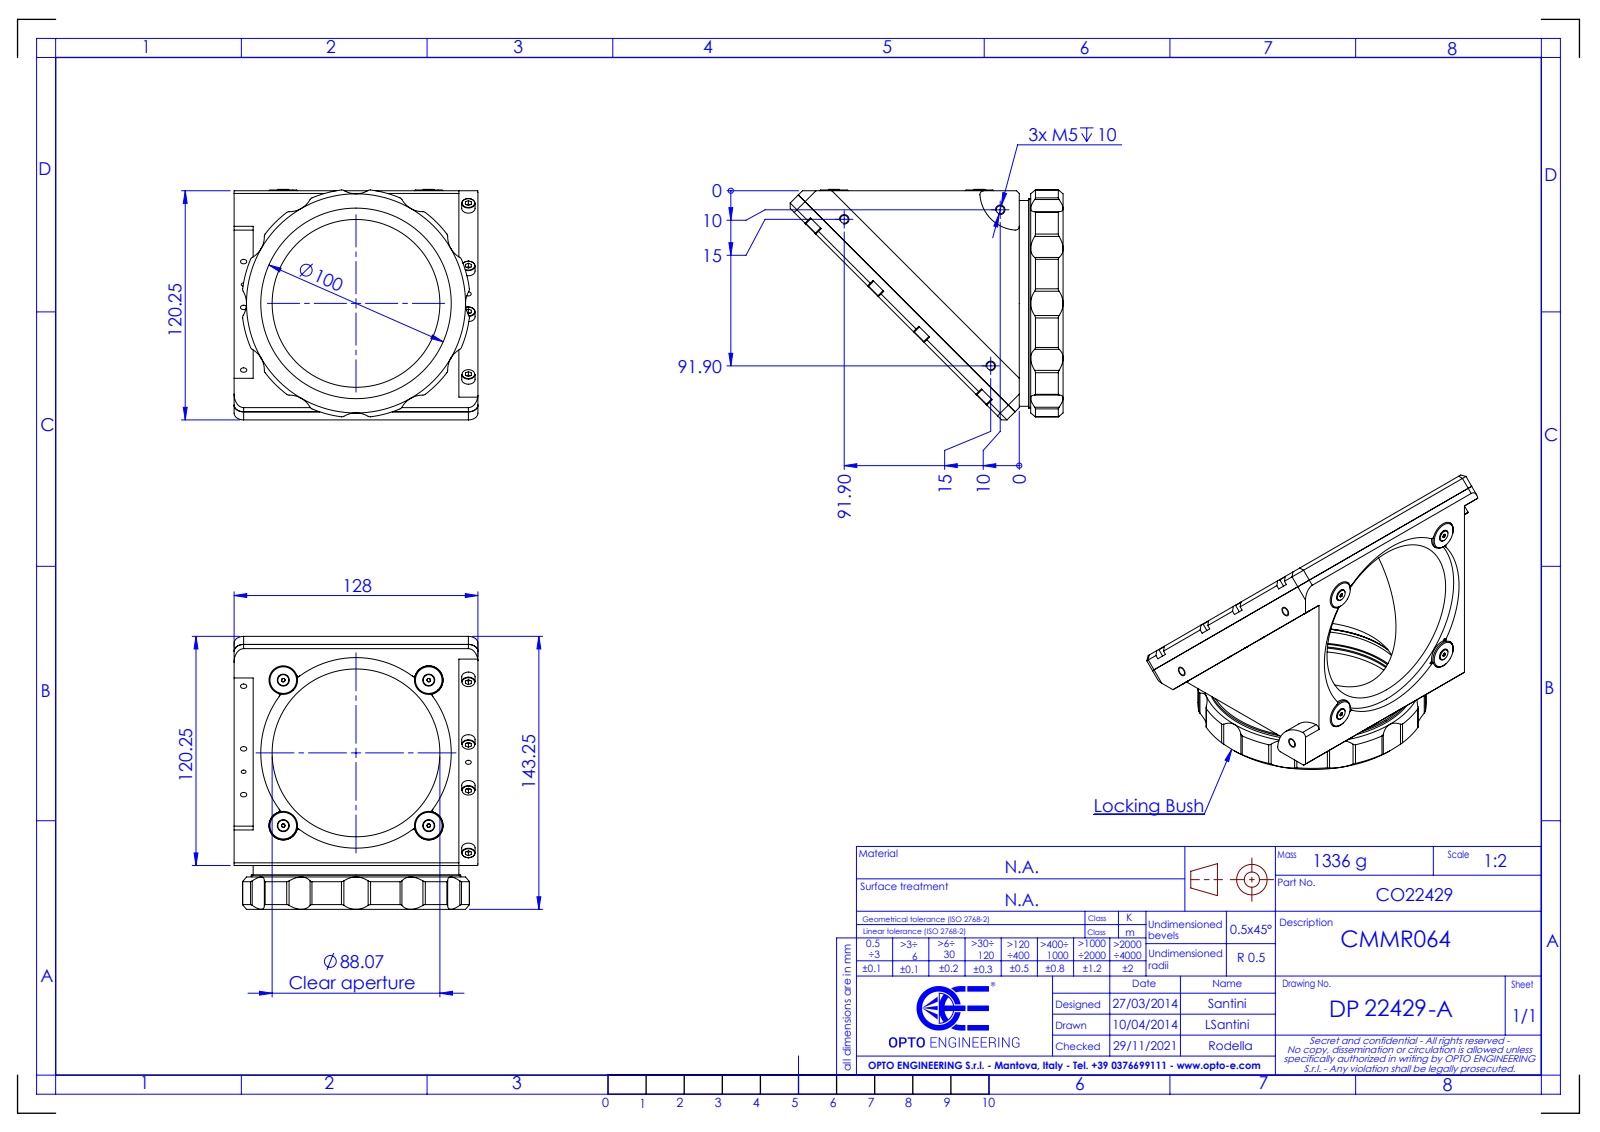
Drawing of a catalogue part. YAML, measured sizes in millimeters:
part_name: "DP22429 -A_CMMR064"
step_written_by: "SolidWorks 2021 (CONFIG_CONTROL_DESIGN)"
units: millimeters
bodies: {solids: 0, faces: 406, planar: 138, cylindrical: 178, other: 90}
overall_size: [143.25, 128, 120.98]
round_holes:
  - {diameter: 3.3, count: 8}
  - {diameter: 4.2, count: 3}
  - {diameter: 3, count: 2}
  - {diameter: 15, count: 2}
  - {diameter: 88.07, count: 2}
  - {diameter: 100, count: 2}
  - {diameter: 2.5, count: 1}
  - {diameter: 100.6, count: 1}
  - {diameter: 102.2, count: 1}
  - {diameter: 104, count: 1}
  - {diameter: 108, count: 1}
round_bosses_or_shafts:
  - {diameter: 7, count: 8}
  - {diameter: 5.75, count: 4}
  - {diameter: 15, count: 2}
  - {diameter: 110, count: 1}
partial_cylinders:
  - {radius: 2, count: 26}
  - {radius: 12.5, count: 12}
  - {radius: 1, count: 8}
  - {radius: 4, count: 4}
  - {radius: 5, count: 4}
  - {radius: 20, count: 1}
  - {radius: 60, count: 1}
face_to_face_distances: [8, 10, 118, 108, 7, 15, 23, 3.8, 11.8, 4]
hole_center_spacings: [118, 17, 46.47, 63.47, 80.47, 119.22, 126.82, 133.99]
